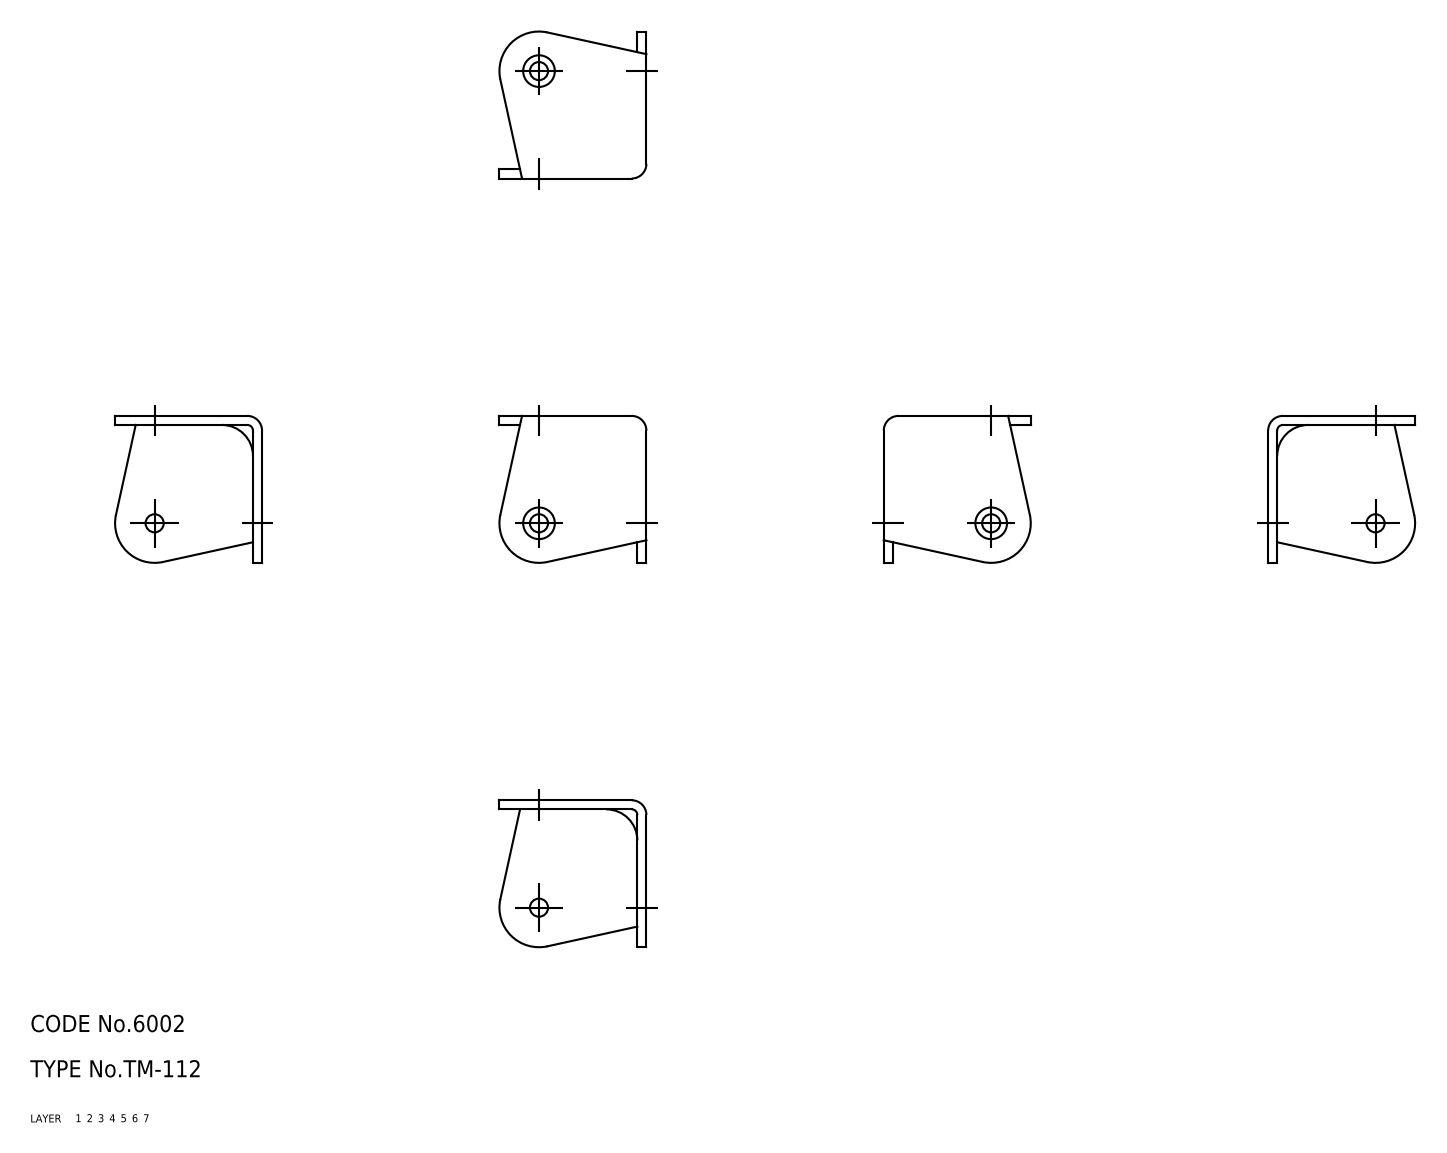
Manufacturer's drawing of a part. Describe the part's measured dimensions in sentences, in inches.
The part is named "angle". Its 3-D file was written by "CADfix (AUTOMOTIVE_DESIGN)". It is 1 solid with 35 faces: 0 planar, 0 cylindrical and 35 other. Overall it measures 1.024 by 1.024 by 1.024 inches. Its volume is 0.145 cubic inches and its surface area 5.064 square inches.
